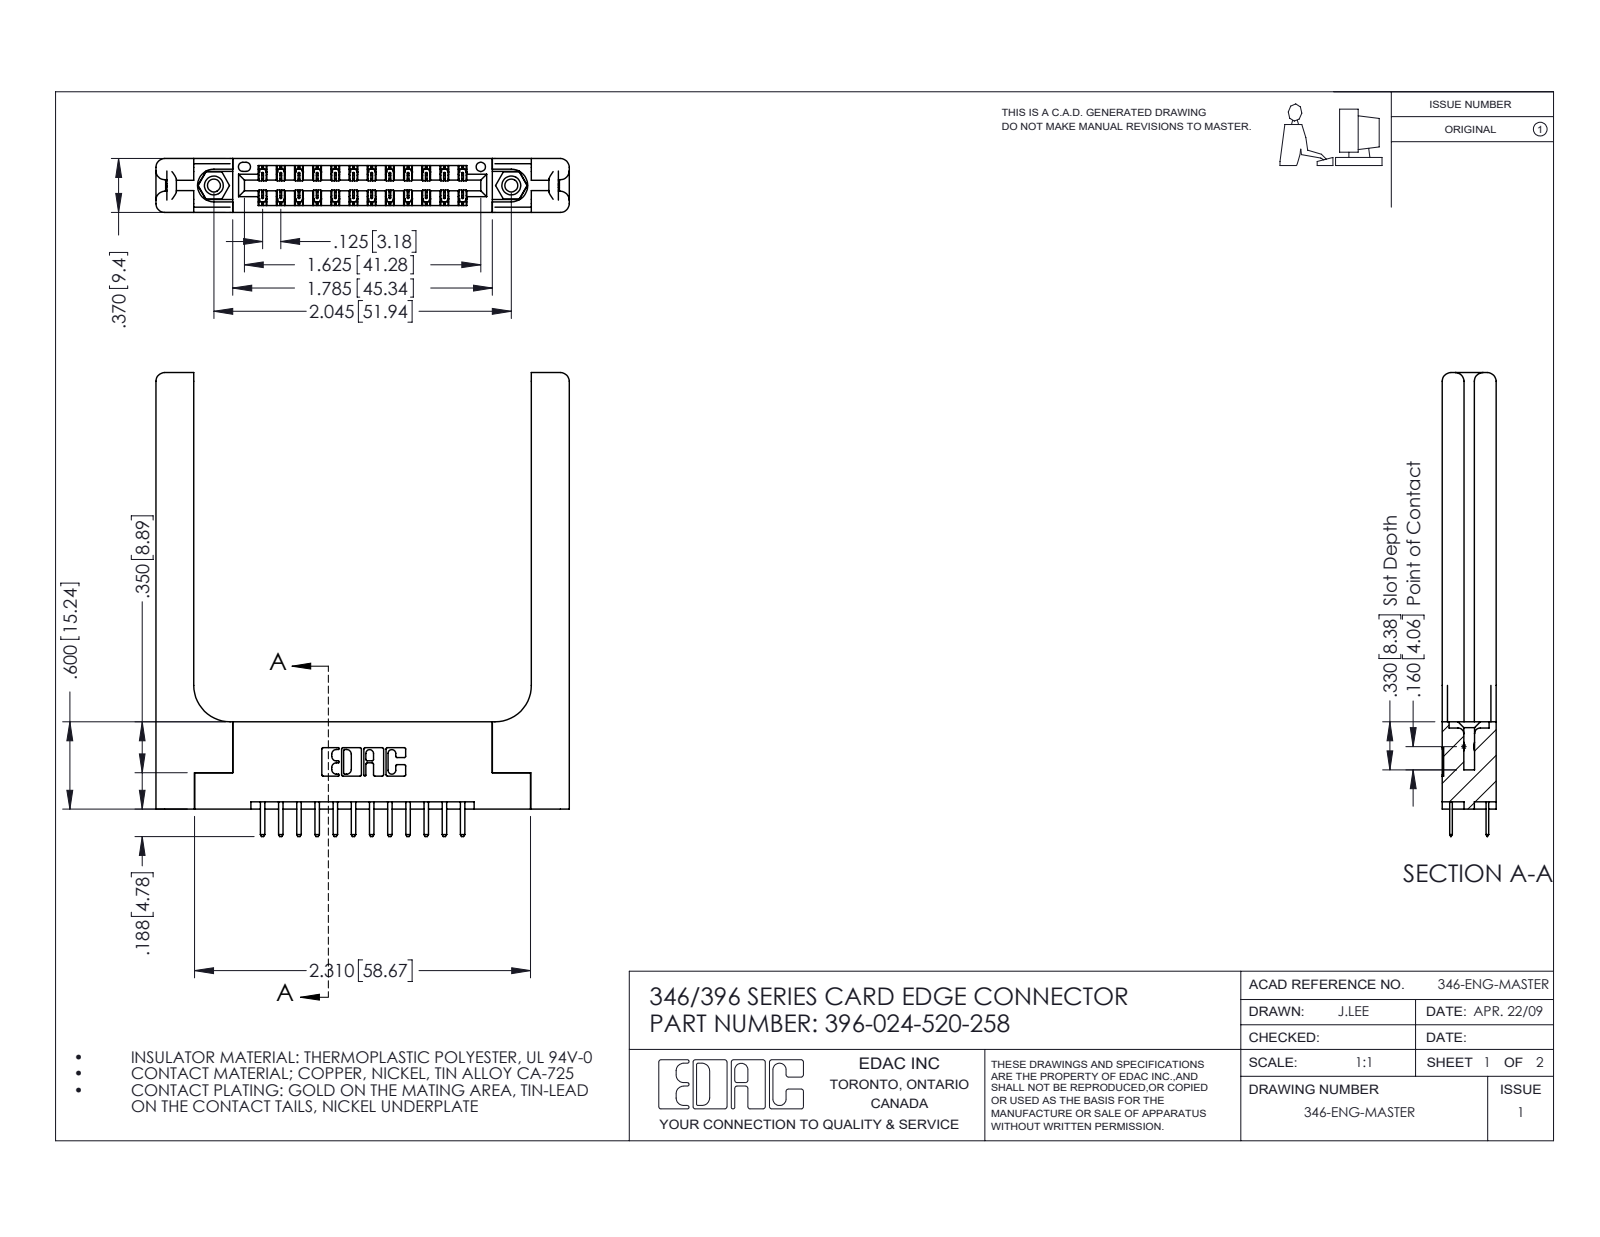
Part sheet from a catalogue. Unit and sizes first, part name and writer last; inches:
Units: inches
Overall size (bounding box): 3.188 × 2.841 × 0.37
Round holes (diameter × count): ⌀0.089 ×2, ⌀0.125 ×2, ⌀0.156 ×2, ⌀0.064 ×1
Round bosses / shafts (diameter × count): ⌀0.155 ×2
Partial cylindrical surfaces — rounded edges, fillets, slot ends (radius × count): R0.006 ×36, R0.01 ×28, R0.01 ×22, R0.06 ×16, R0.007 ×6, R0.031 ×6, R0.026 ×3, R0.014 ×2
Main face-to-face distances: 0.37, 0.15, 0.072, 0.148, 0.25, 0.048, 0.322, 0.102, 0.22, 0.173
Hole centre spacings: 0.246, 1.839, 2.045
Volume: 0.872 in³ · Surface area: 21.41 in²
Bodies: 29 solids, 1722 faces (1112 planar, 550 cylindrical, 60 other)
Part name (STEP PRODUCT): 396-024-520-258; 346-220-058_345-220-058; 346 Part_Flush Mounting Lugs - 0.156 Dia-TH; 345-250-001_345-250-001-102 (+1 more)
STEP written by: SolidWorks 2016 (CONFIG_CONTROL_DESIGN)
